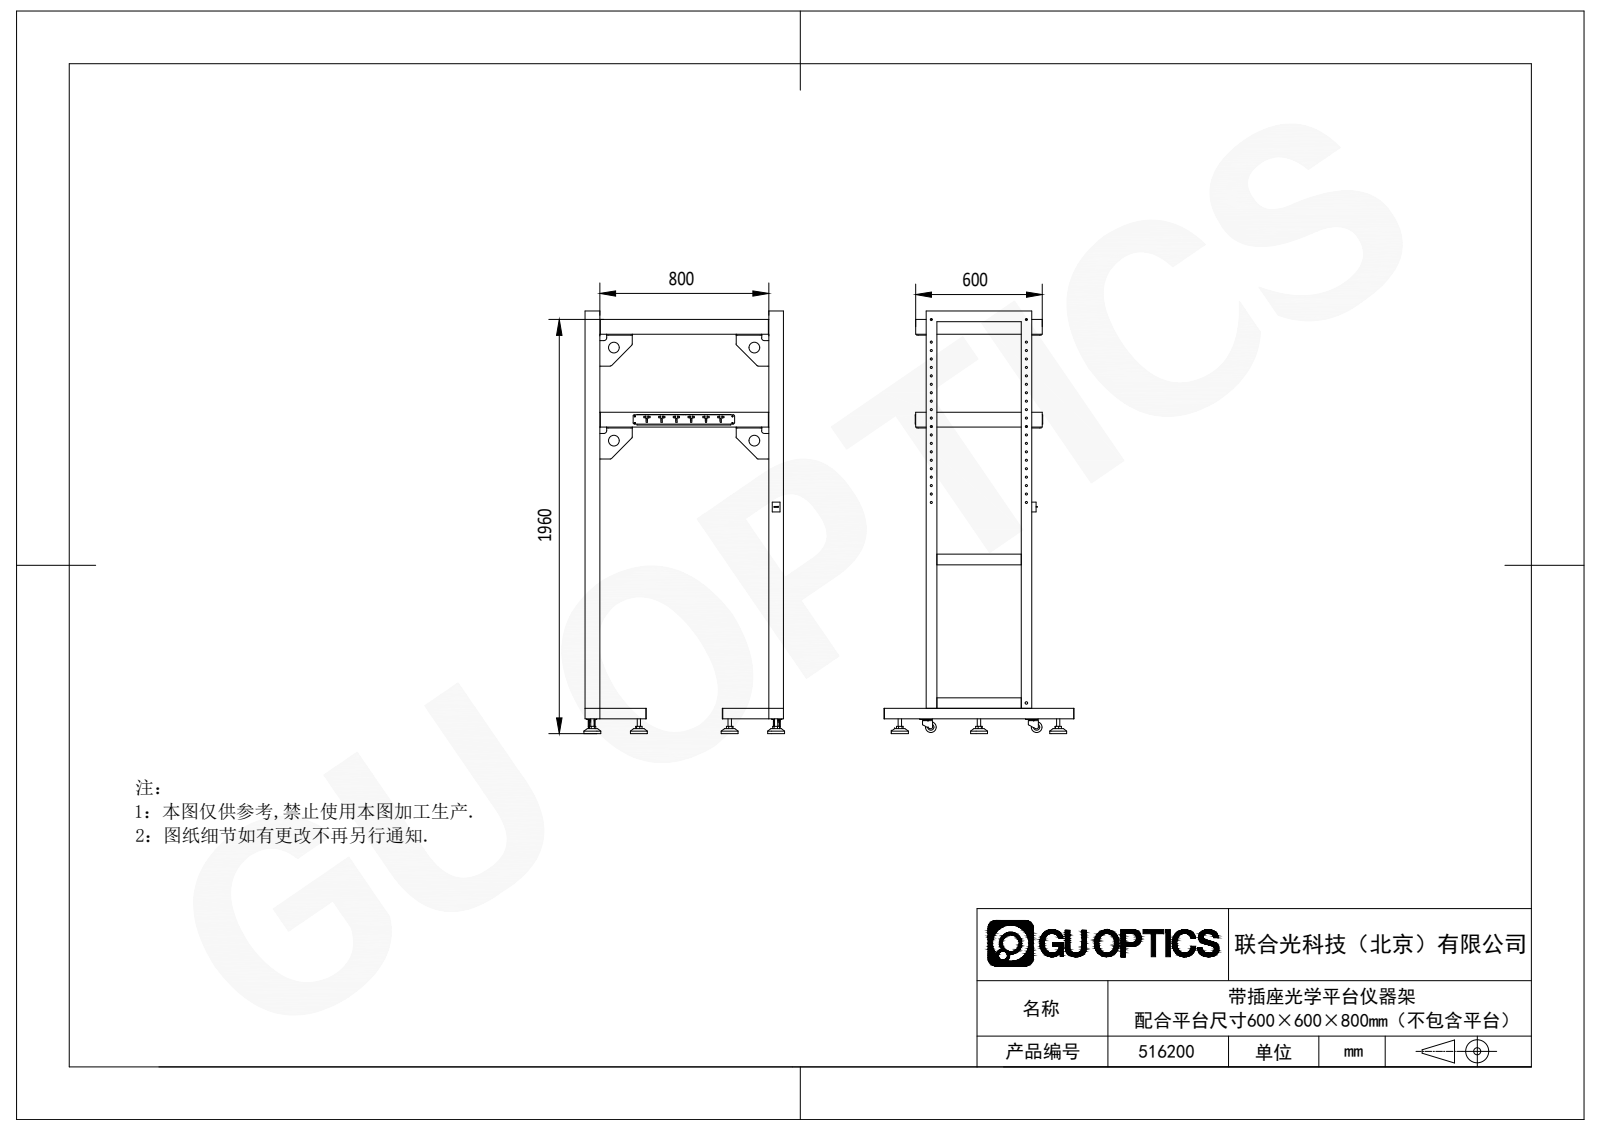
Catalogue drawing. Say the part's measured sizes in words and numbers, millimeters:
The part is named "516200". Its 3-D file was written by "SolidWorks 2020 (CONFIG_CONTROL_DESIGN)". It is 57 solids with 2175 faces: 1135 planar, 964 cylindrical and 76 other. Overall it measures 2001 by 950 by 900 millimeters. Its volume is 15 660 000 cubic millimeters and its surface area 10 790 000 square millimeters. Round holes: 66 of diameter 9, 16 of diameter 6.1, 16 of diameter 10, 8 of diameter 4.2, 6 of diameter 6.5, 6 of diameter 17, 6 of diameter 18, 6 of diameter 26, 6 of diameter 69, 4 of diameter 3.2, 4 of diameter 5.2, 4 of diameter 6. Round bosses or shafts: 6 of diameter 80, 6 of diameter 16, 4 of diameter 26, 4 of diameter 18, 2 of diameter 50, 2 of diameter 10. Partial cylindrical surfaces (rounded edges, fillets, slot ends): 28 of radius 5, 24 of radius 7, 16 of radius 3, 8 of radius 1.5, 8 of radius 1.51, 8 of radius 4.01, 6 of radius 4.25, 4 of radius 13. The main face-to-face distances are 2, 3, 50, 70, 870, 48, 450, 440, 67, 1.5. The hole center spacings are 40, 80, 120, 160, 200, 280, 240, 320.
